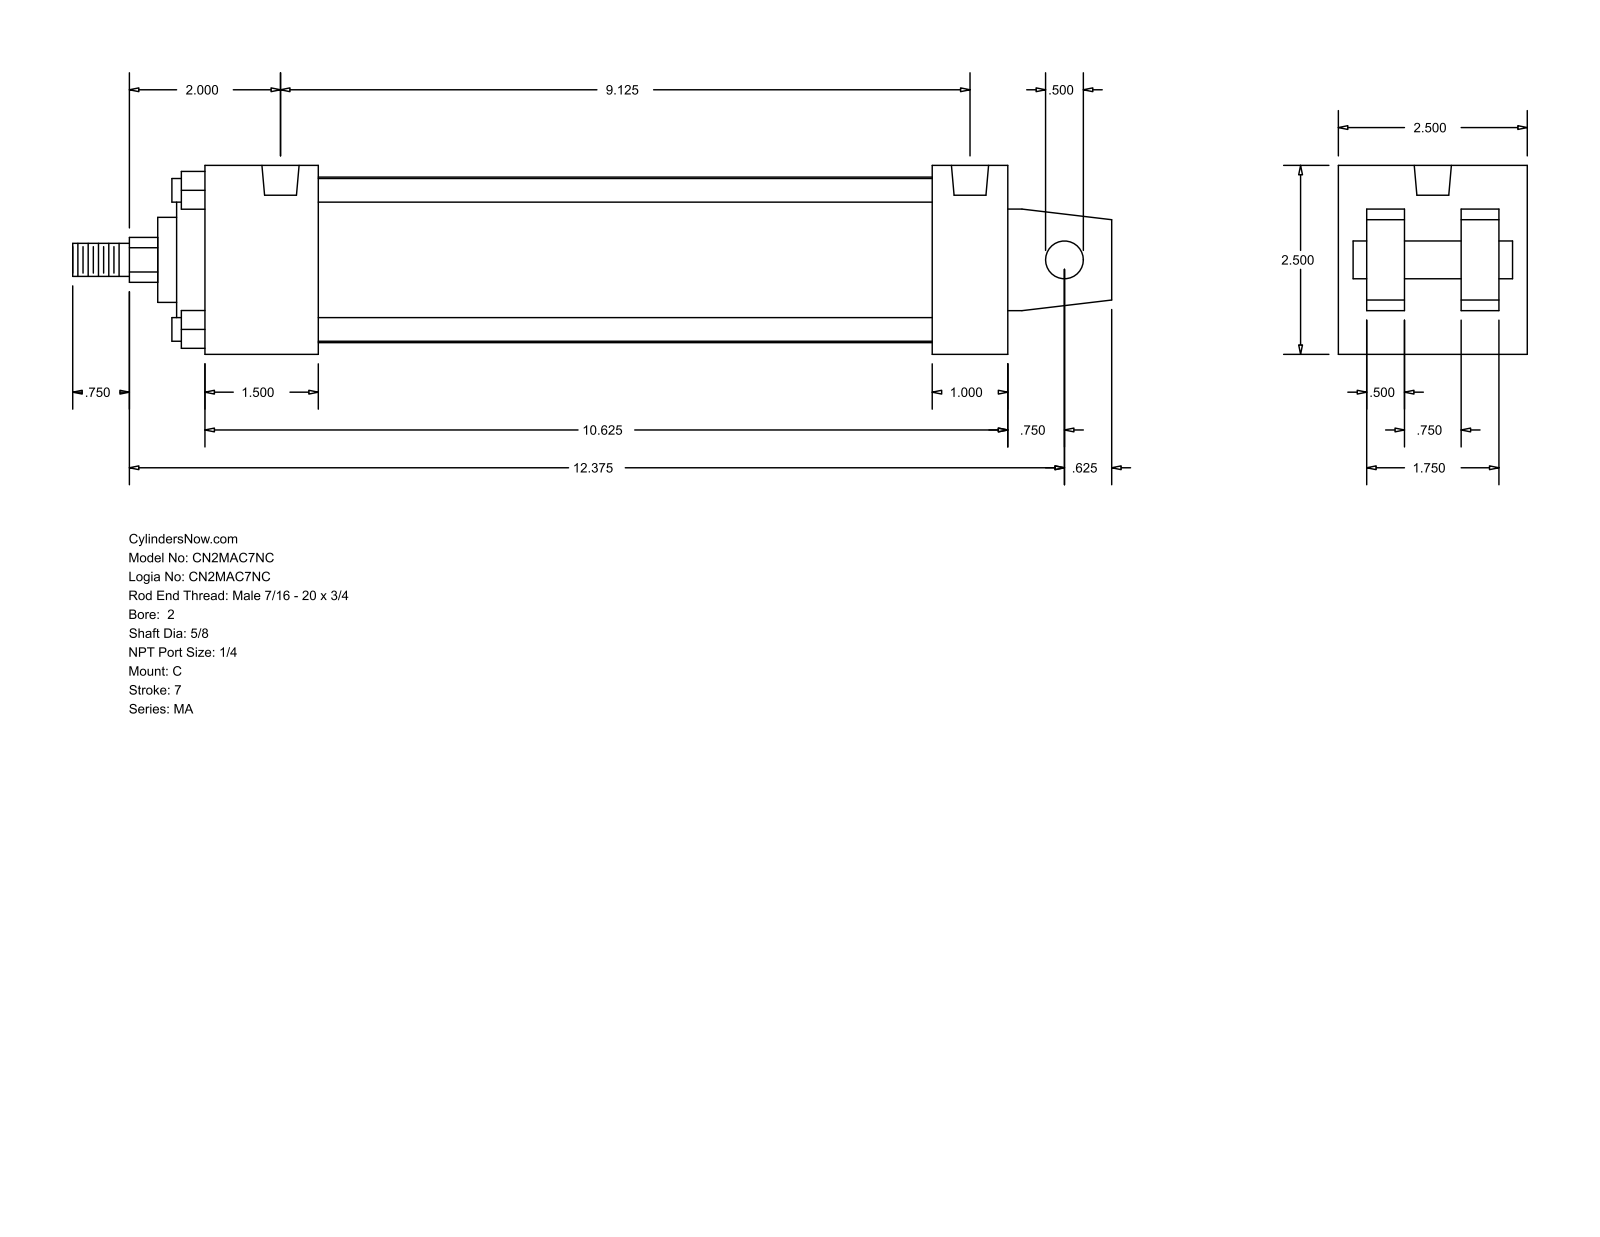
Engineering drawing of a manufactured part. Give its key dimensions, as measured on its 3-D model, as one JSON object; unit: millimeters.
{"part_name": "MA_C__0200_0.625", "step_written_by": "GSSL Pune (CONFIG_CONTROL_DESIGN)", "units": "millimeters", "bodies": {"solids": 0, "faces": 105, "planar": 77, "cylindrical": 28, "other": 0}, "overall_size": [349.25, 63.5, 63.5], "round_holes": [[7.94, 4], [12.49, 2]], "round_bosses_or_shafts": [[7.94, 4], [55.63, 1], [50.8, 1], [28.57, 1], [15.88, 1], [12.7, 1], [11.11, 1]], "partial_cylinders_radius": [[7.54, 1]], "face_to_face_distances": [63.5, 9.52, 12.7, 22.22, 41.28, 53.98, 31.76, 38.1, 269.87, 231.77], "hole_center_spacings": [231.77]}
